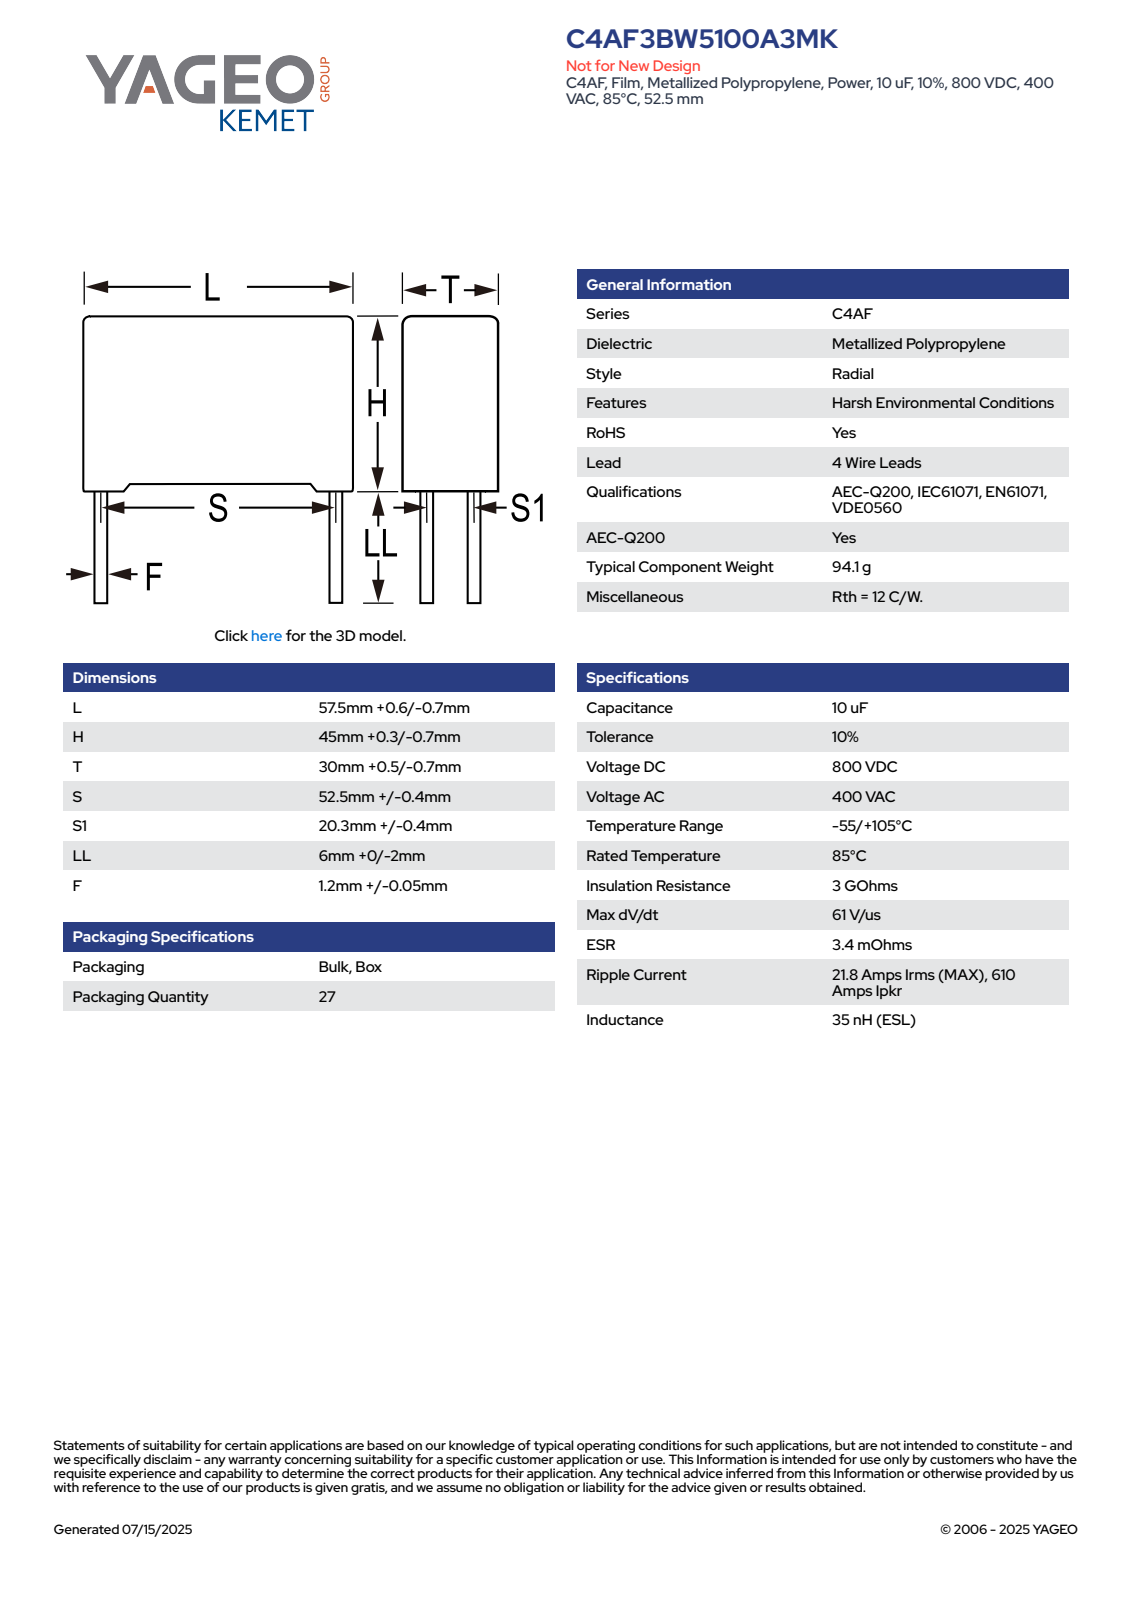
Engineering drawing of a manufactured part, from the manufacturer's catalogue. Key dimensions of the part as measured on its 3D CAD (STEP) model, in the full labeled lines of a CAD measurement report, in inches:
Part name (STEP PRODUCT): CFP_RB4_57.5X45X30_L58.1H45.3T30.5S52.5S120.3LL6F1.25
STEP written by: SolidWorks 2021 (AUTOMOTIVE_DESIGN)
Units: inches
Bodies: 4 solids, 87 faces (79 planar, 8 cylindrical, 0 other)
Overall size (bounding box): 2.287 × 2.02 × 1.201
Volume: 4.77 in³ · Surface area: 18.44 in²
Round bosses / shafts (diameter × count): ⌀0.049 ×4
Main face-to-face distances: 1.201, 1.731, 2.287, 0.052, 1.783, 1.201, 0.074, 2.214, 2.14, 1.127
